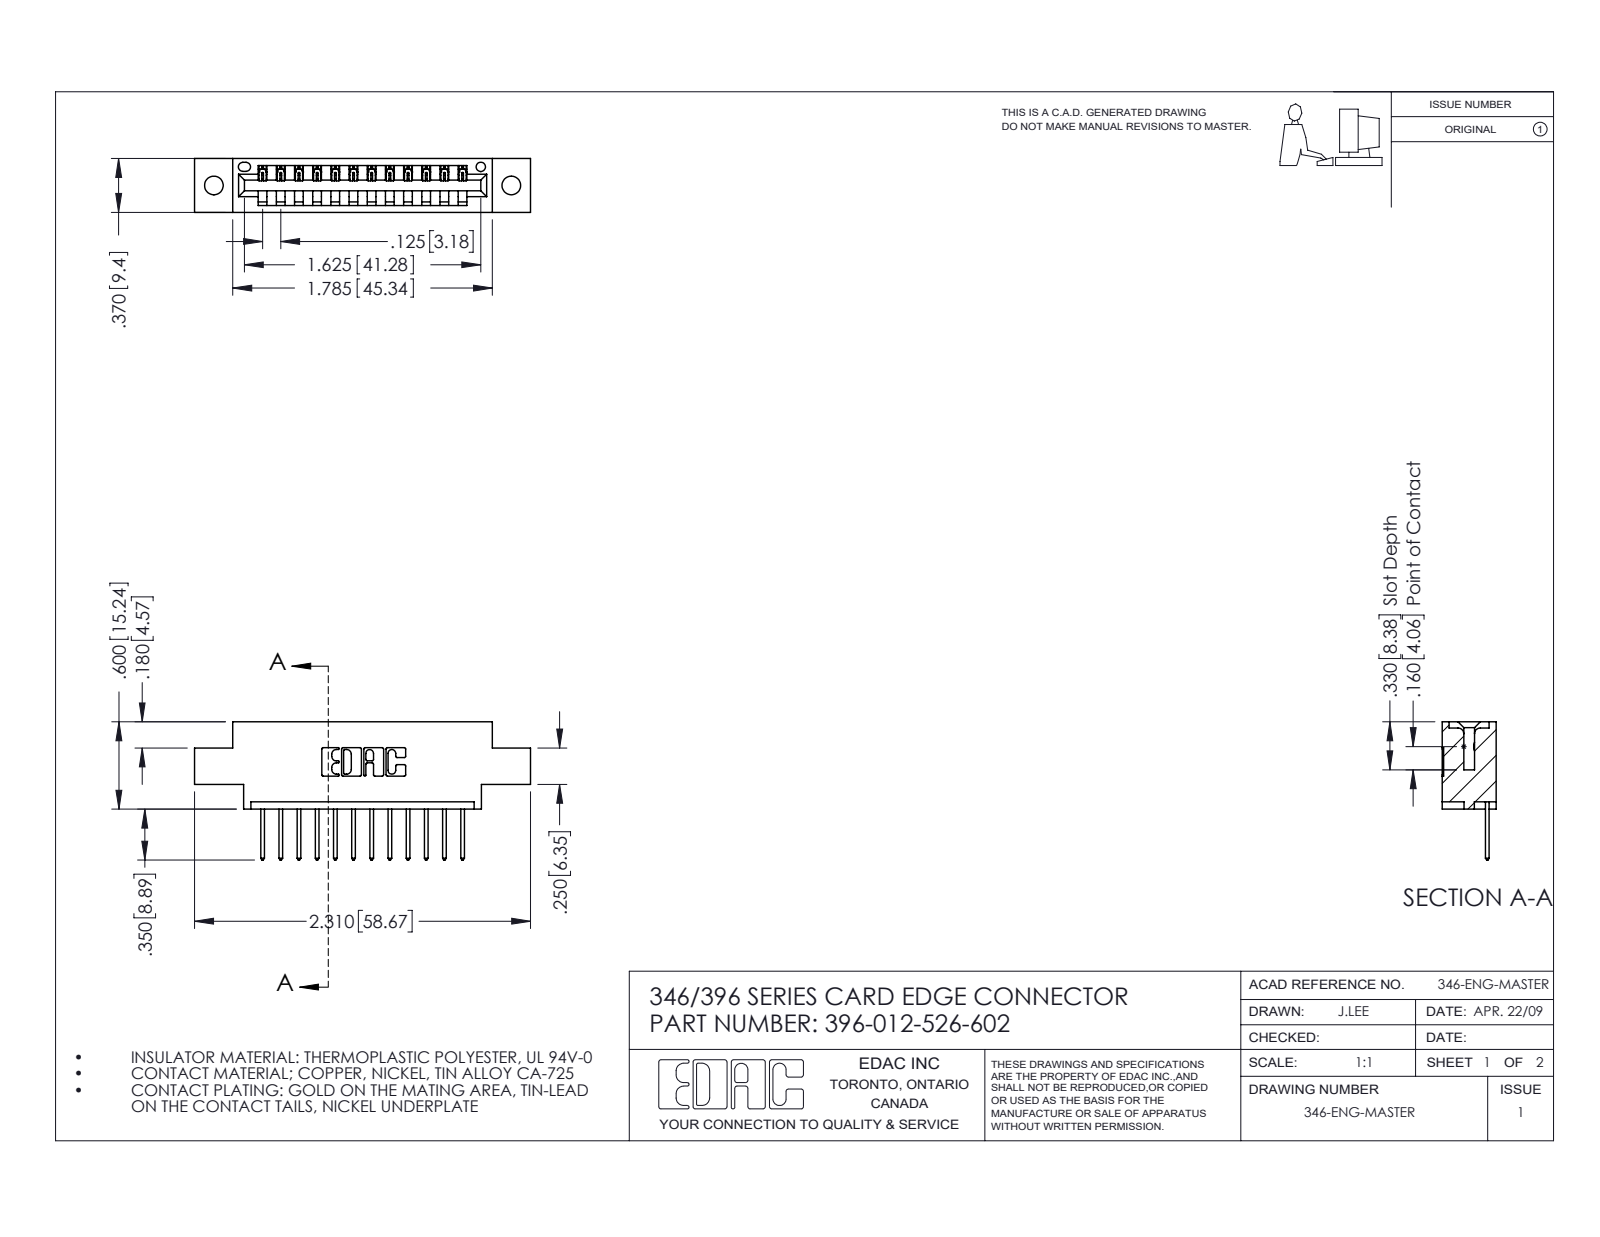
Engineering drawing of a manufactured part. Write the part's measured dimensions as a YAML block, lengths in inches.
part_name: "345-292-001_345-293-126; 396-012-526-602; 346 Part_0.170 Offset - 0.128 Dia"
step_written_by: "SolidWorks 2016 (CONFIG_CONTROL_DESIGN)"
units: inches
bodies: {solids: 13, faces: 822, planar: 560, cylindrical: 262, other: 0}
overall_size: [2.31, 0.95, 0.37]
volume: 0.318
surface_area: 9.399
round_holes:
  - {diameter: 0.128, count: 2}
  - {diameter: 0.064, count: 1}
partial_cylinders:
  - {radius: 0.006, count: 24}
  - {radius: 0.01, count: 24}
  - {radius: 0.01, count: 22}
  - {radius: 0.007, count: 6}
  - {radius: 0.031, count: 6}
  - {radius: 0.026, count: 3}
  - {radius: 0.031, count: 2}
  - {radius: 0.04, count: 2}
face_to_face_distances: [0.25, 0.37, 0.048, 0.322, 0.072, 0.298, 0.025, 0.148, 0.222, 0.1]
hole_center_spacings: [0.246, 1.839, 2.045]
